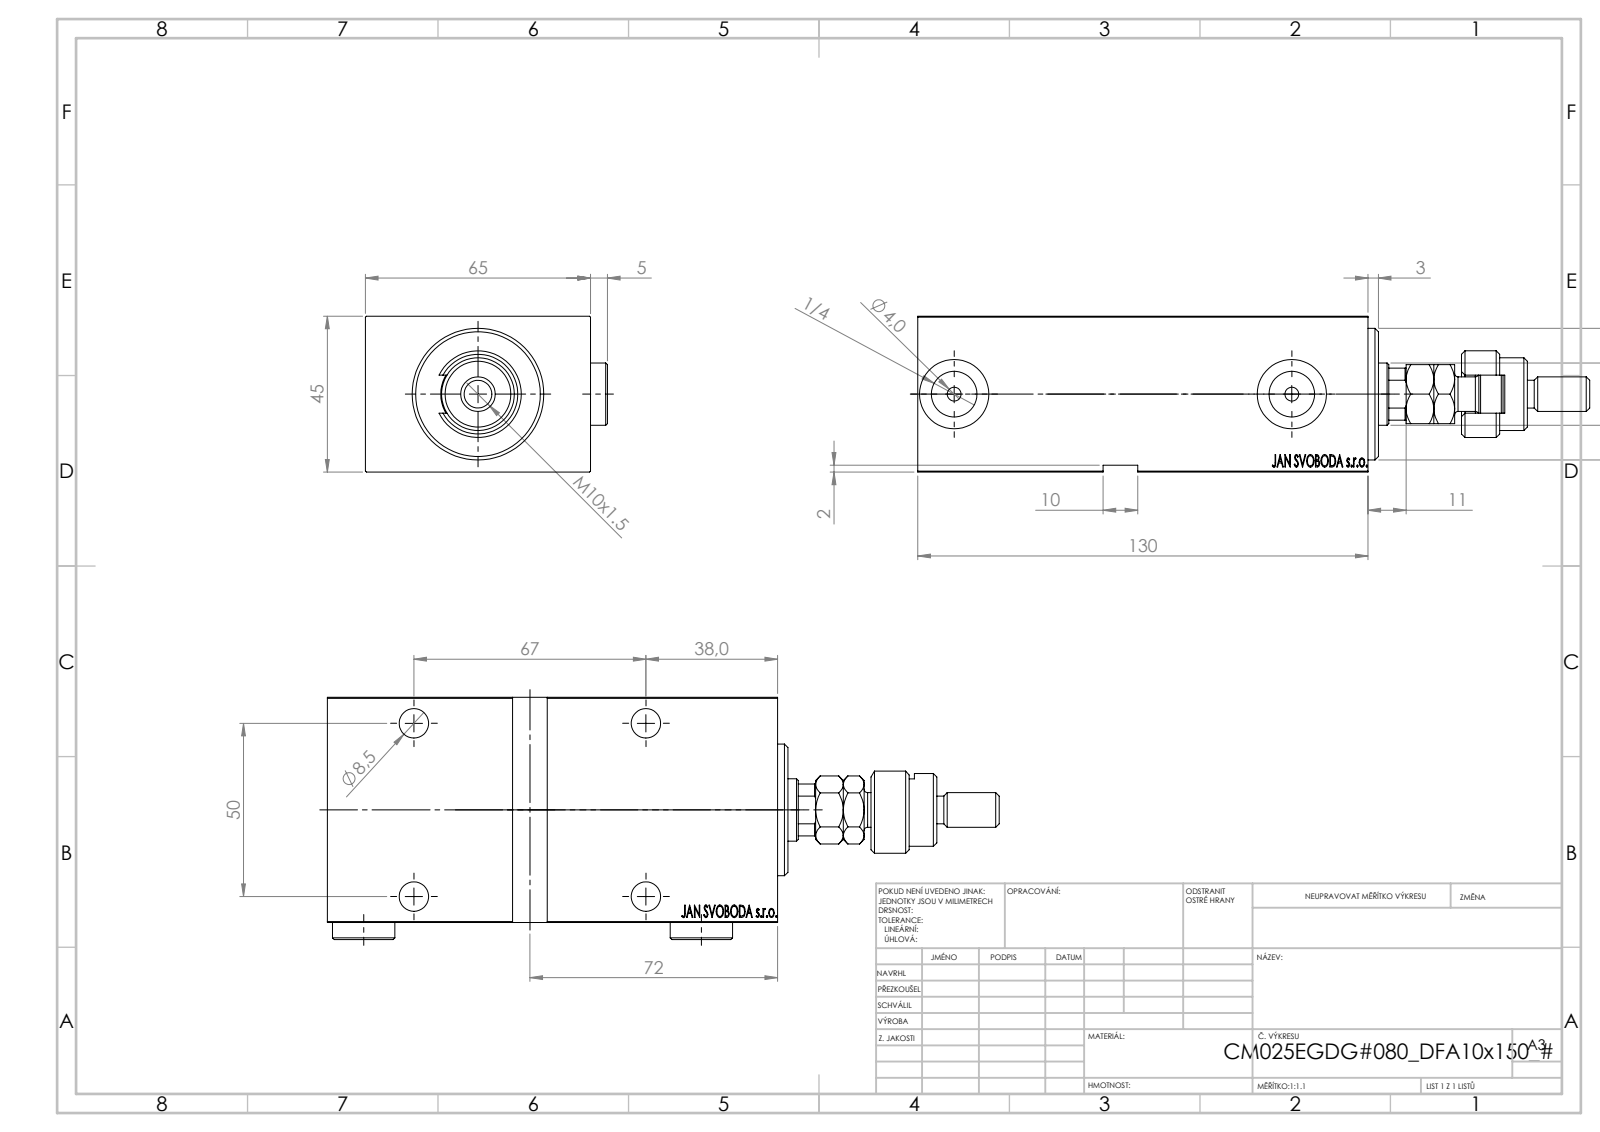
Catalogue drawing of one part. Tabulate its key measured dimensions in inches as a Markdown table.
| quantity | value |
| --- | --- |
| part name | FEMALE_PART_FOR_DFA; V450CM_E_VCP; V450CM_E_Body; V450CM_VC_B (+2 more) |
| STEP written by | SolidWorks 2019 (CONFIG_CONTROL_DESIGN) |
| units | inches |
| bodies | 7 solids, 995 faces (472 planar, 81 cylindrical, 442 other) |
| overall size | 7.638 × 2.752 × 1.772 |
| volume | 21.88 in³ |
| surface area | 114.1 in² |
| round holes (diameter × count) | 0.335 × 5, 0.531 × 4, 0.157 × 2, 0.518 × 2, 0.787 × 2, 0.709 × 1, 0.846 × 1, 1.378 × 1 |
| round bosses / shafts (diameter × count) | 0.709 × 2, 1.496 × 1, 1.063 × 1, 0.984 × 1, 0.827 × 1, 0.63 × 1, 0.394 × 1, 0.315 × 1 |
| partial cylindrical surfaces (radius × count) | 0.217 × 1, 0.335 × 1, 0.344 × 1 |
| main face-to-face distances | 1.772, 2.559, 5.118, 0.197, 2.555, 0.236, 0.315, 0.079, 4.882, 1.693 |
| hole center spacings | 1.969, 2.638, 3.291, 3.839 |
